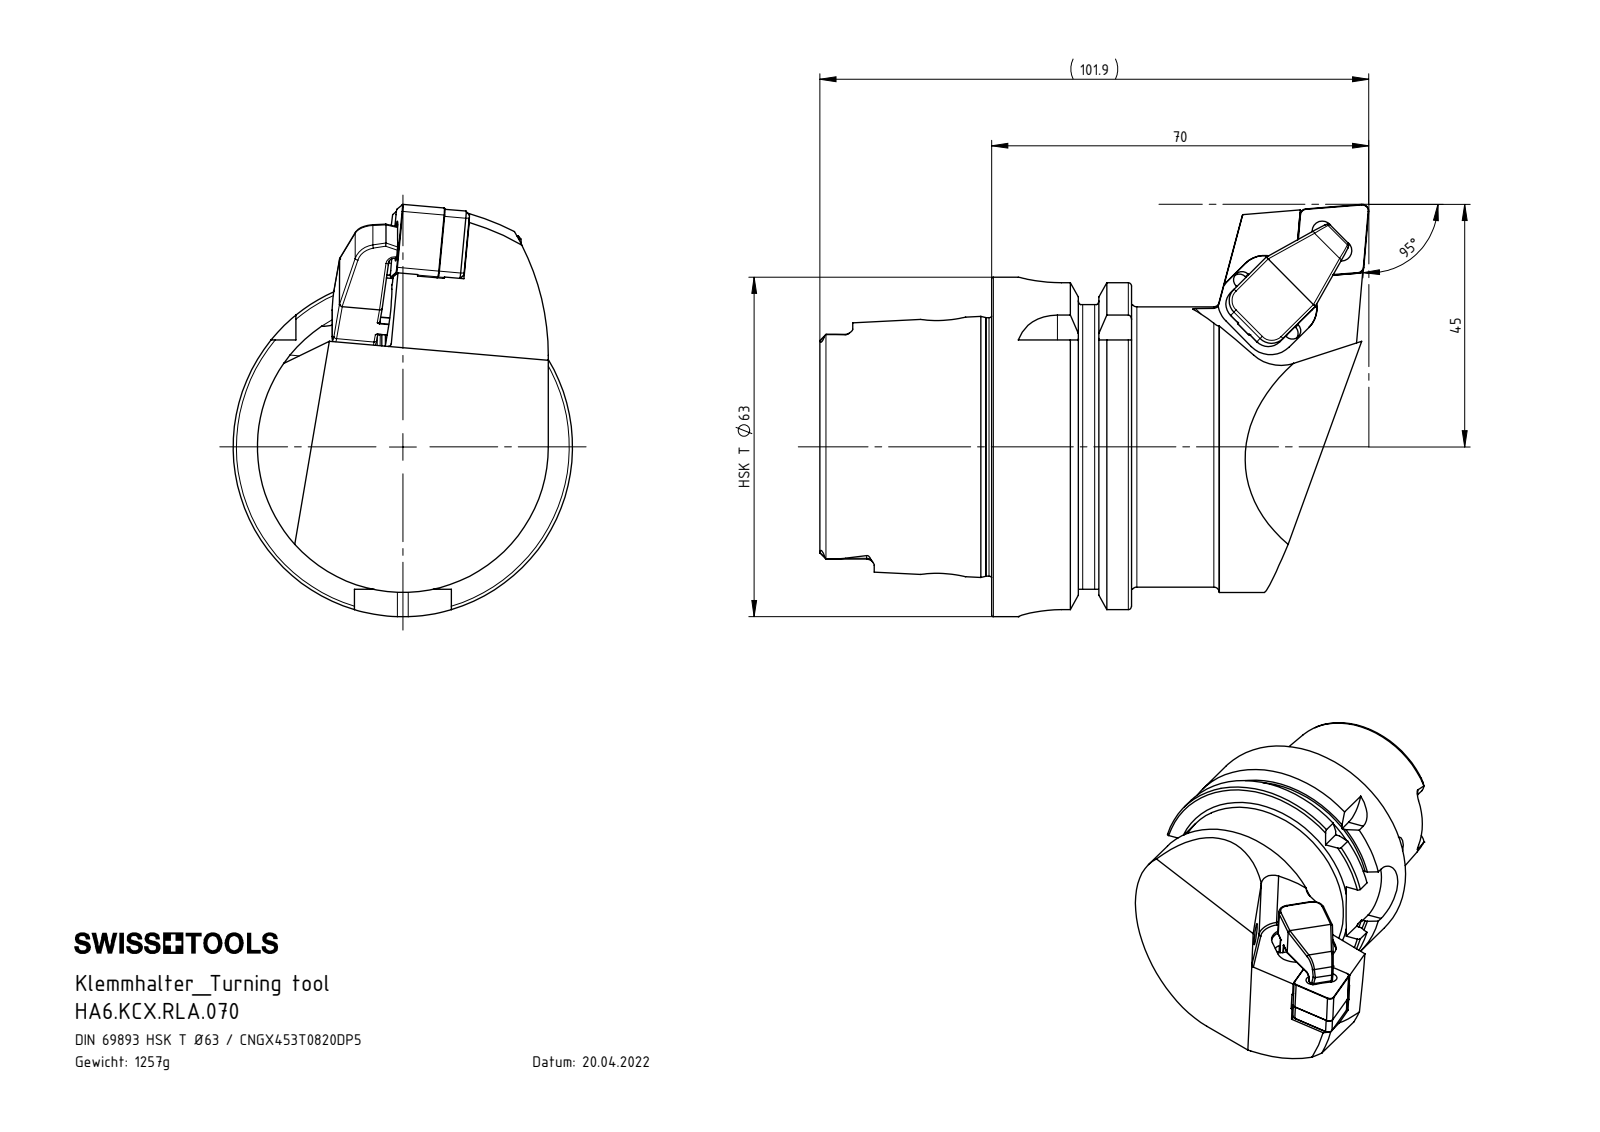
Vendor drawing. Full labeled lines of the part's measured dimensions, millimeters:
Part name (STEP PRODUCT): CNGX453T0820DP5 SX6; Torx T20 M6x12; HA6-KCX.RLA.070_A; KVT_MB_600_060 (+3 more)
STEP written by: SolidWorks 2017 (AUTOMOTIVE_DESIGN)
Units: millimetres
Bodies: 6 solids, 252 faces (54 planar, 92 cylindrical, 106 other)
Overall size (bounding box): 71.99 × 47.05 × 26.51
Volume: 5 679 mm³ · Surface area: 5 562 mm²
Round holes (diameter × count): ⌀5 ×1, ⌀7.35 ×1, ⌀8 ×1
Round bosses / shafts (diameter × count): ⌀6 ×2, ⌀10 ×1, ⌀8 ×1
Partial cylindrical surfaces — rounded edges, fillets, slot ends (radius × count): R0.1 ×25, R0.5 ×14, R0.42 ×6, R0.65 ×6, R1.2 ×5, R1.19 ×4, R3 ×2, R1 ×1
Main face-to-face distances: 12.7, 17.09, 7.93, 9.16, 9.09, 1.16, 8, 4.7, 12.63, 13.79
